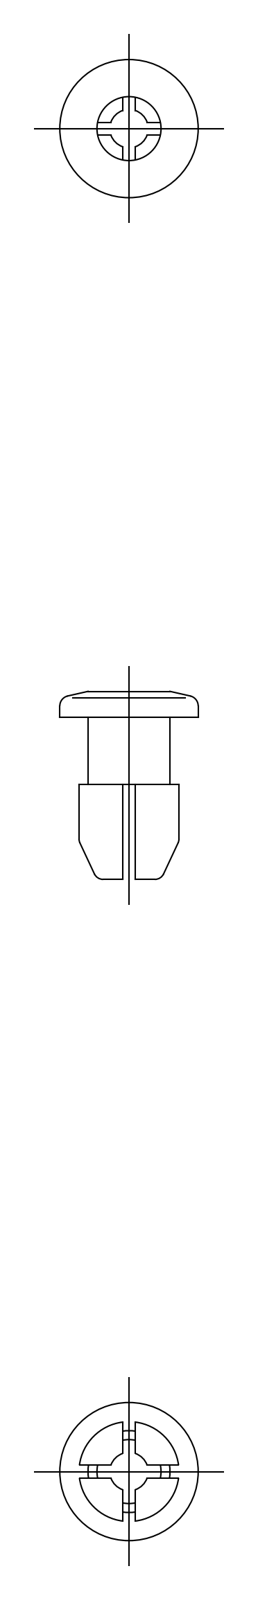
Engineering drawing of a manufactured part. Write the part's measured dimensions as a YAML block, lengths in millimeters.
part_name: "grommet"
step_written_by: "CADfix (AUTOMOTIVE_DESIGN)"
units: millimeters
bodies: {solids: 1, faces: 56, planar: 0, cylindrical: 0, other: 56}
overall_size: [14.7, 10.8, 10.8]
volume: 343
surface_area: 726
